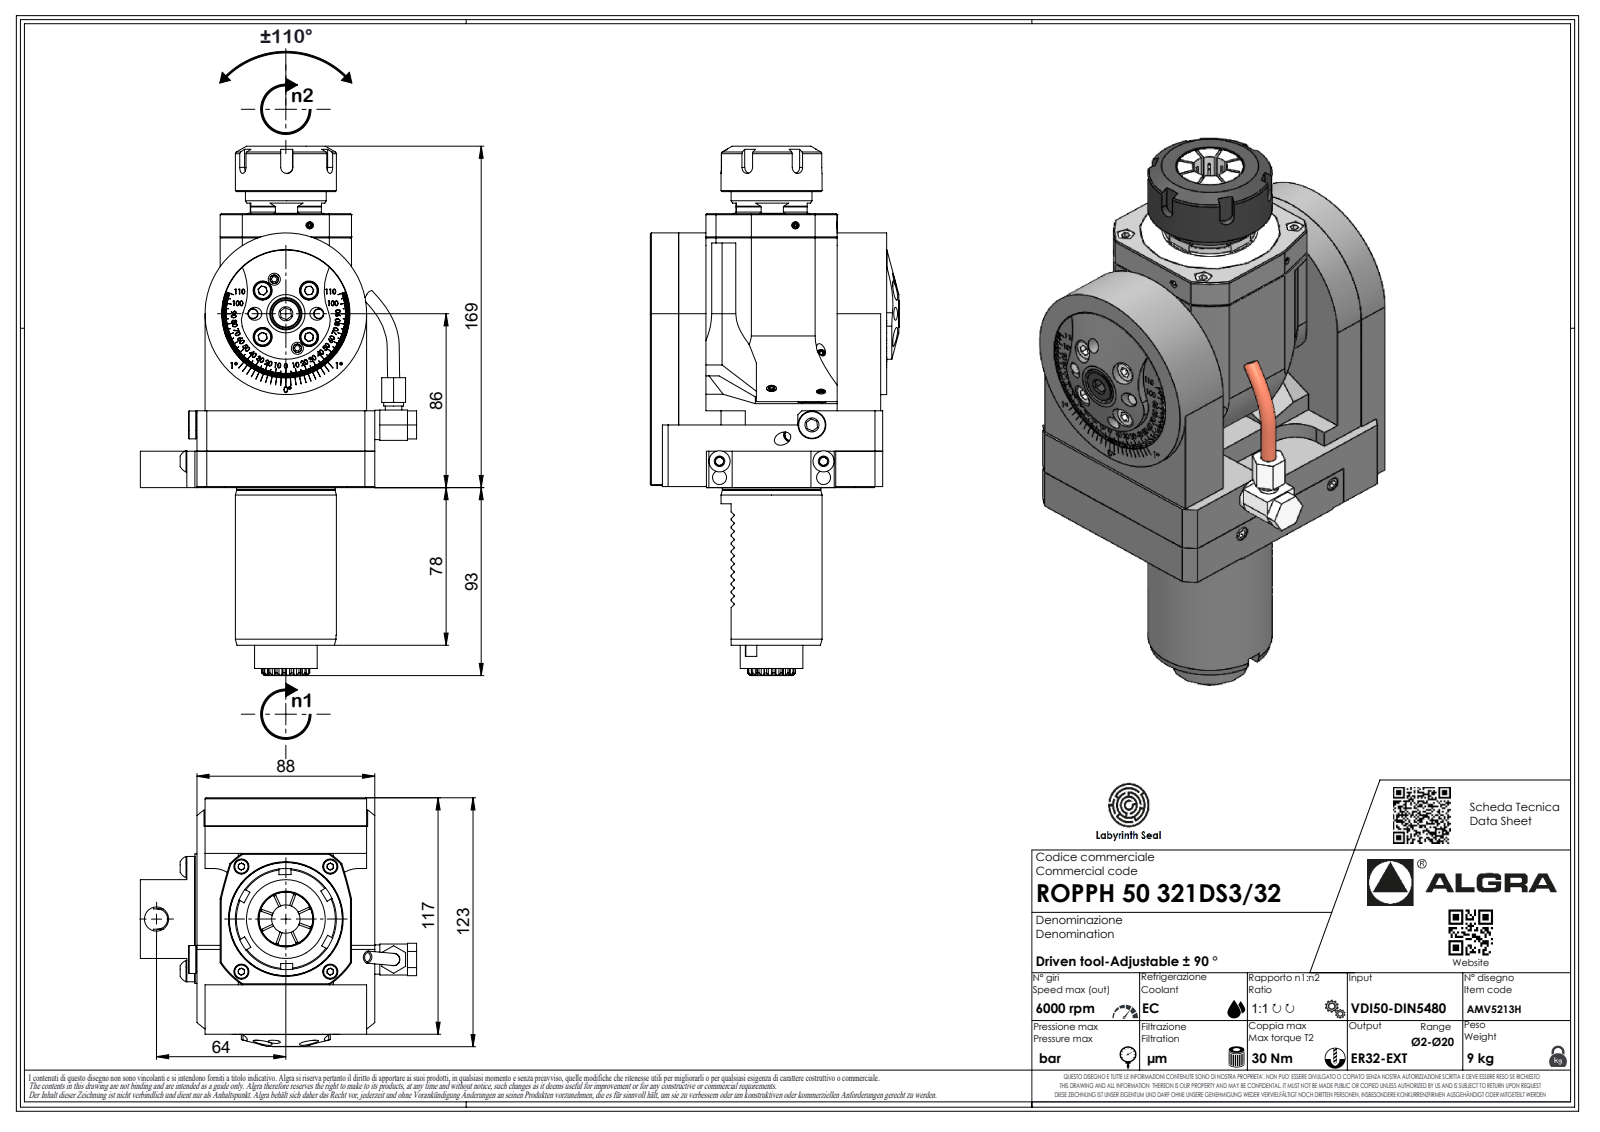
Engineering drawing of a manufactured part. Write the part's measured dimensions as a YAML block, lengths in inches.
part_name: "ROPPH50321DS332"
step_written_by: "SolidWorks 2023 (AUTOMOTIVE_DESIGN)"
units: inches
bodies: {solids: 1, faces: 752, planar: 427, cylindrical: 147, other: 178}
overall_size: [10.311, 5.382, 4.843]
volume: 78.05
surface_area: 175.3
round_holes:
  - {diameter: 0.083, count: 1}
  - {diameter: 1.417, count: 1}
round_bosses_or_shafts:
  - {diameter: 3.15, count: 1}
  - {diameter: 1.969, count: 1}
  - {diameter: 1.917, count: 1}
  - {diameter: 1.575, count: 1}
  - {diameter: 1.377, count: 1}
  - {diameter: 1.22, count: 1}
  - {diameter: 0.571, count: 1}
  - {diameter: 0.386, count: 1}
partial_cylinders:
  - {radius: 0.063, count: 36}
  - {radius: 0.012, count: 12}
  - {radius: 0.013, count: 7}
  - {radius: 0.02, count: 7}
  - {radius: 0.146, count: 7}
  - {radius: 0.118, count: 5}
  - {radius: 0.394, count: 2}
  - {radius: 0.472, count: 2}
face_to_face_distances: [0.157, 2.559, 3.307, 0.453, 0.02, 2.854, 3.012, 0.295, 1.083, 3.524]
